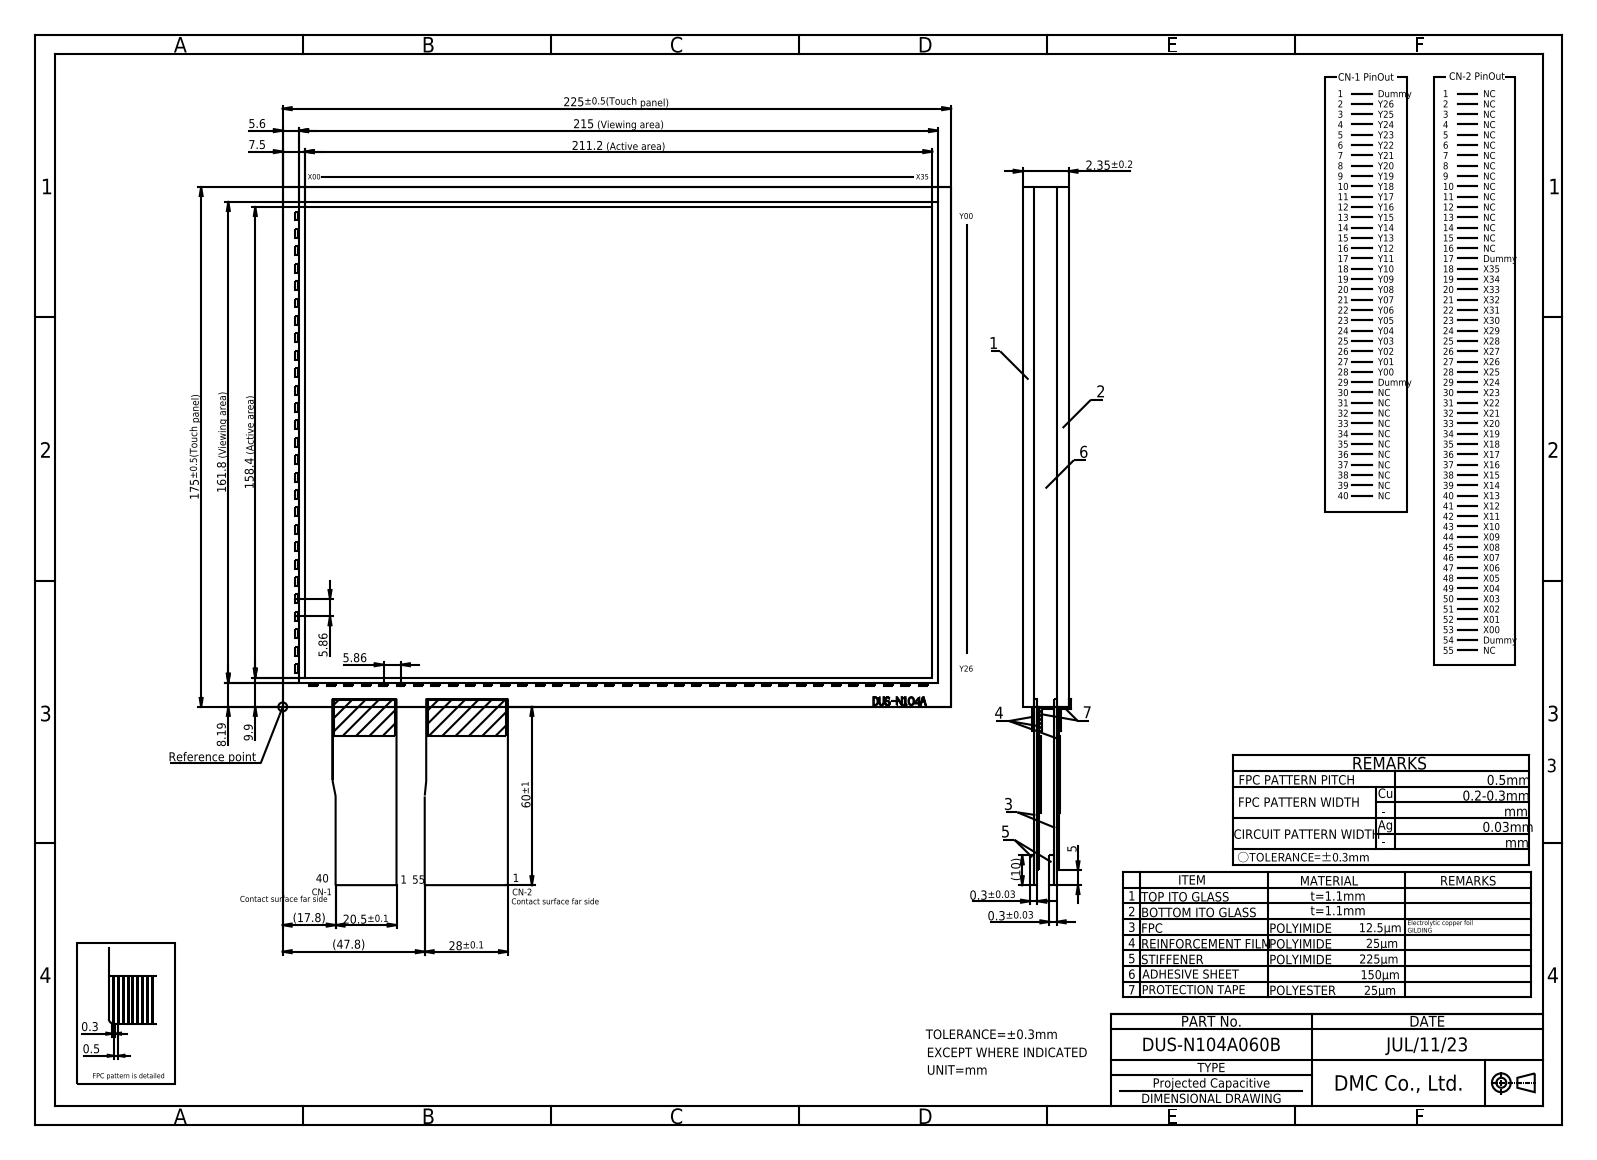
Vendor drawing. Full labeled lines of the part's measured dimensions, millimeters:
Part name (STEP PRODUCT): DUS-N104A060B
STEP written by: Autodesk Inventor 2020 (CONFIG_CONTROL_DESIGN)
Units: millimetres
Bodies: 1 solid, 422 faces (416 planar, 6 cylindrical, 0 other)
Overall size (bounding box): 315 × 270 × 2.35
Volume: 92 885 mm³ · Surface area: 86 732 mm²
Partial cylindrical surfaces — rounded edges, fillets, slot ends (radius × count): R0.2 ×4, R5 ×2
Main face-to-face distances: 2.35, 1.12, 1.23, 1.25, 1.1, 1, 2.25, 1.13, 175, 0.8
